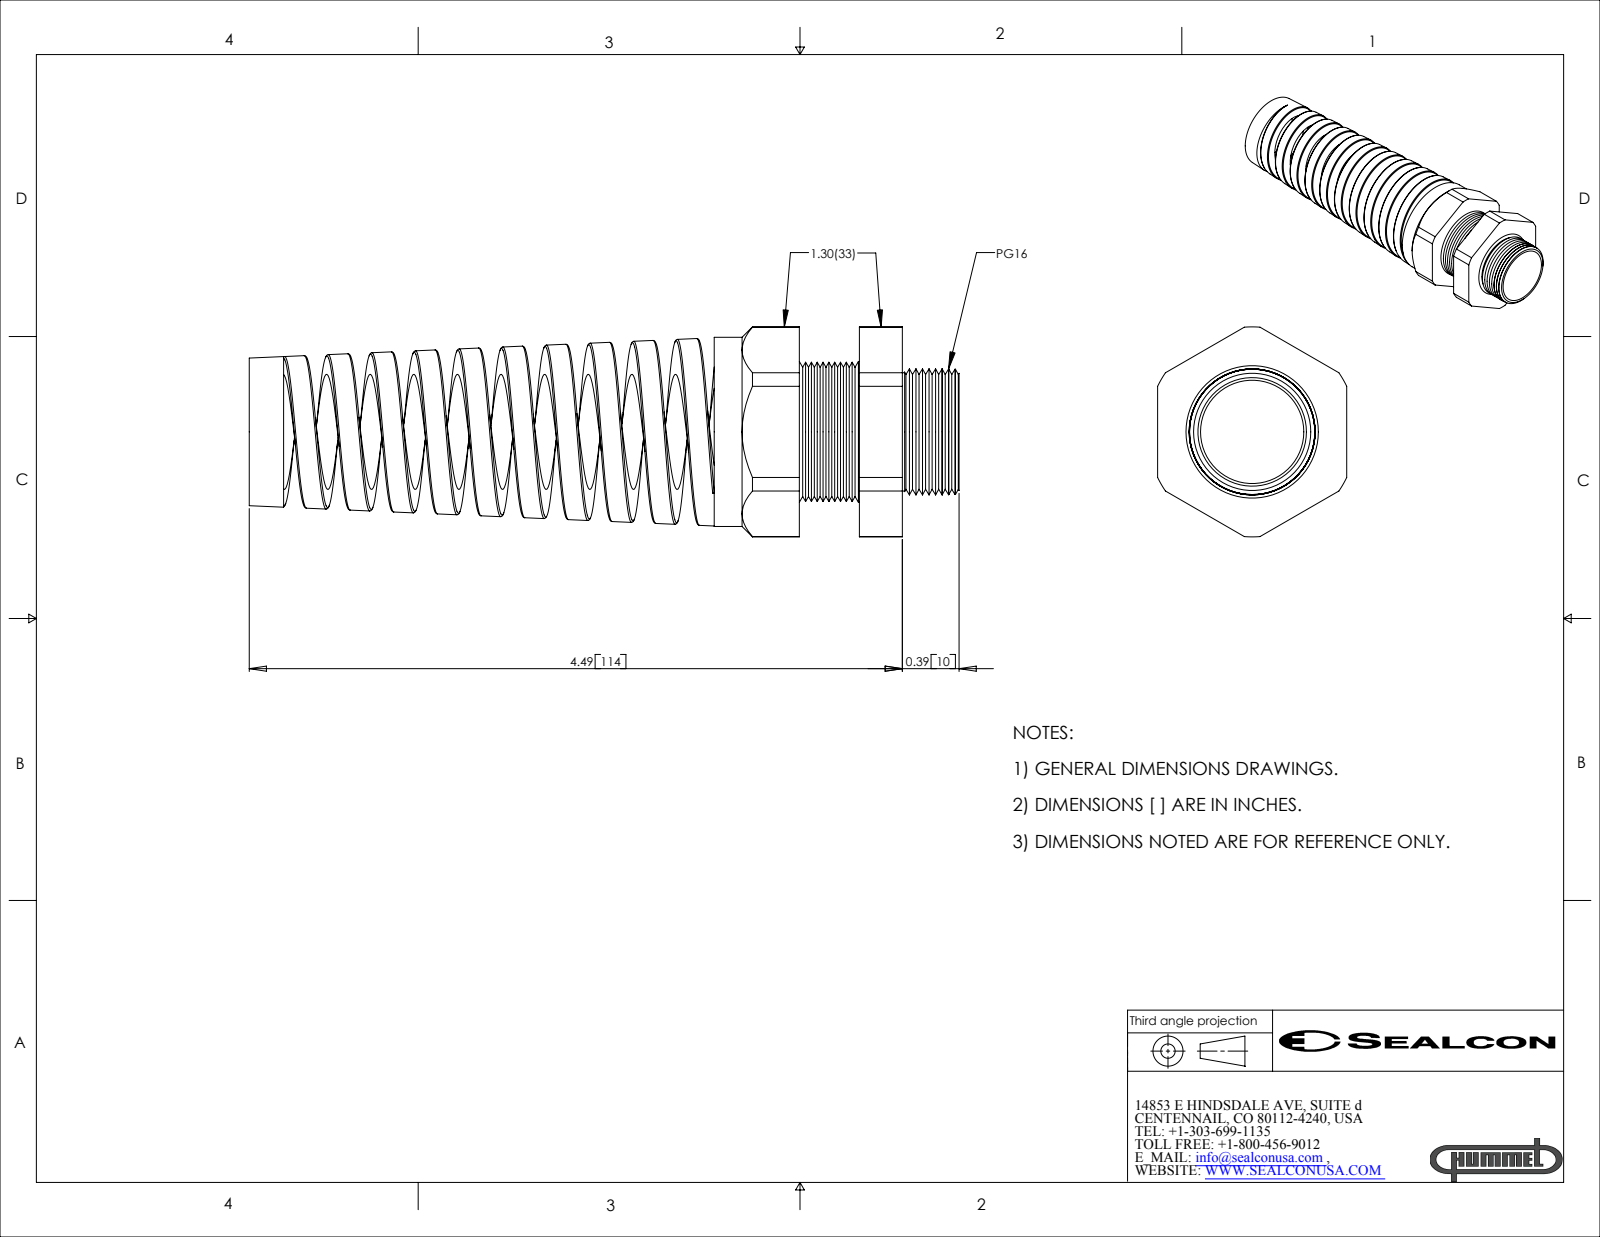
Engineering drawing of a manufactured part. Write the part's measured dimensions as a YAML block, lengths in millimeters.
part_name: "CF16GA-BK"
step_written_by: "SolidWorks 2007 (CONFIG_CONTROL_DESIGN)"
units: millimeters
bodies: {solids: 2, faces: 193, planar: 24, cylindrical: 45, other: 124}
overall_size: [124, 36.7, 33]
volume: 32810
surface_area: 25850
round_holes:
  - {diameter: 18, count: 1}
  - {diameter: 20.1, count: 1}
round_bosses_or_shafts:
  - {diameter: 33, count: 1}
  - {diameter: 24.6, count: 1}
partial_cylinders:
  - {radius: 10.3, count: 1}
  - {radius: 18.3, count: 1}
face_to_face_distances: [33, 18, 10.5, 7.5, 14.9, 25.3, 32.9, 81.2, 96.1, 106.6]
